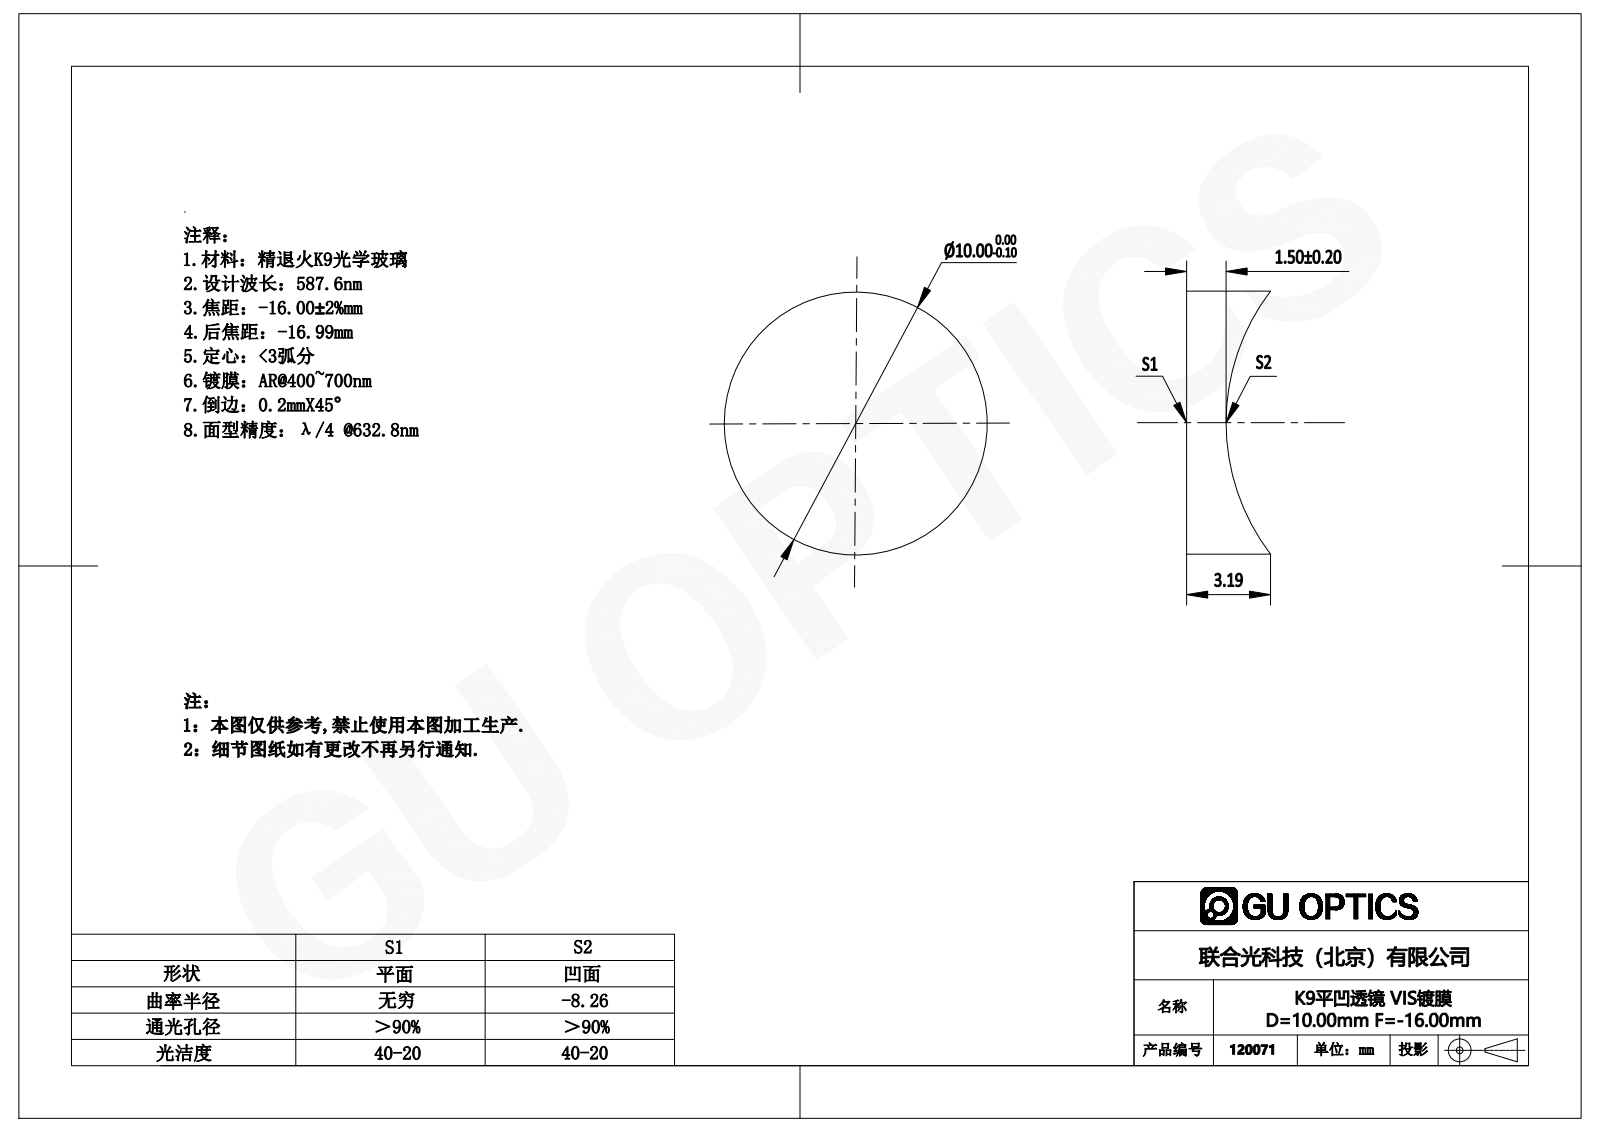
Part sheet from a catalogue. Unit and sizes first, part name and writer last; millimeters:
Units: millimetres
Overall size (bounding box): 10 × 10 × 3.19
Round bosses / shafts (diameter × count): ⌀10 ×1
Volume: 182 mm³ · Surface area: 266 mm²
Bodies: 1 solid, 5 faces (1 planar, 2 cylindrical, 2 other)
Part name (STEP PRODUCT): 120011
STEP written by: SolidWorks 2016 (AUTOMOTIVE_DESIGN)
